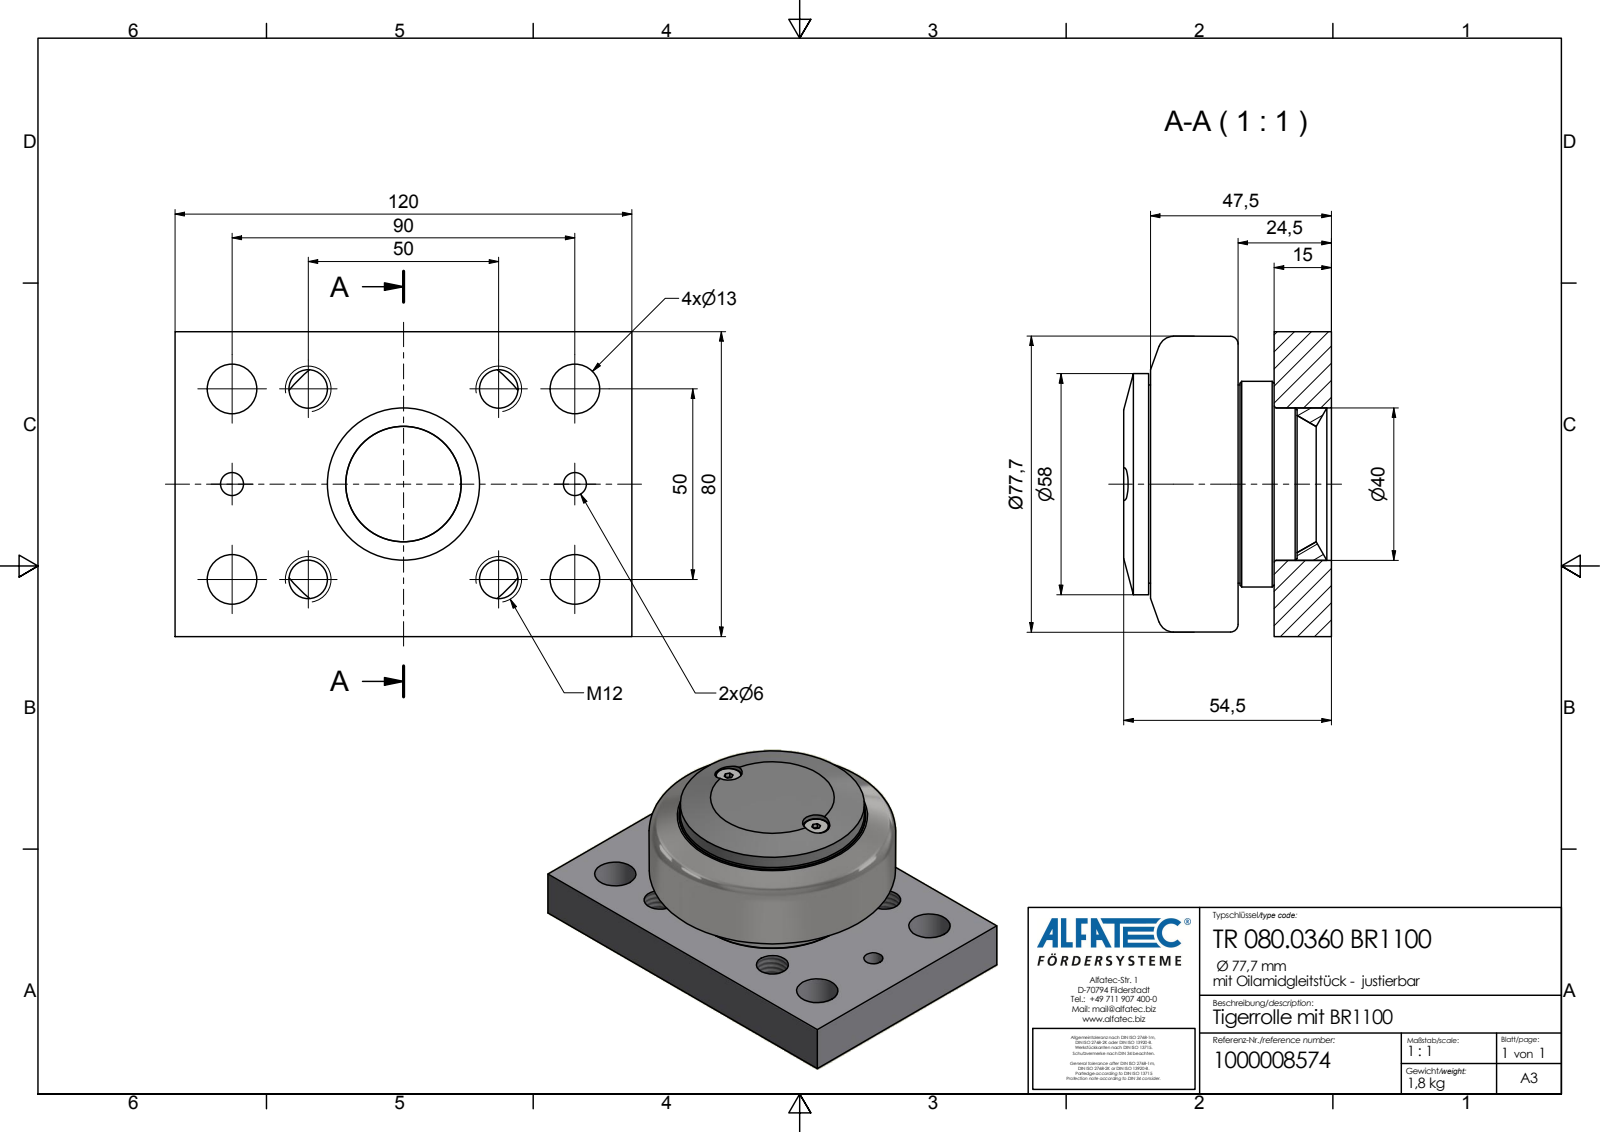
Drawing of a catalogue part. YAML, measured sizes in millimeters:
part_name: "TR 080.0360 BR1100_Kontur"
step_written_by: "Autodesk Inventor 2020 (AP242_MANAGED_MODEL_BASED_3D_ENGINEERING_MIM_LF)"
units: millimeters
bodies: {solids: 1, faces: 57, planar: 28, cylindrical: 19, other: 10}
overall_size: [120, 80, 54.5]
volume: 269094
surface_area: 41997
round_holes:
  - {diameter: 10.11, count: 4}
  - {diameter: 13, count: 4}
  - {diameter: 6, count: 2}
  - {diameter: 8.6, count: 2}
  - {diameter: 40, count: 1}
round_bosses_or_shafts:
  - {diameter: 7.8, count: 2}
  - {diameter: 58, count: 1}
  - {diameter: 54, count: 1}
  - {diameter: 52, count: 1}
face_to_face_distances: [15, 24.5, 9.5, 80, 120, 54.5, 39.5, 30, 4, 11]
hole_center_spacings: [50, 20, 25, 25.6, 32.02, 35.36, 35.71, 51.04]
